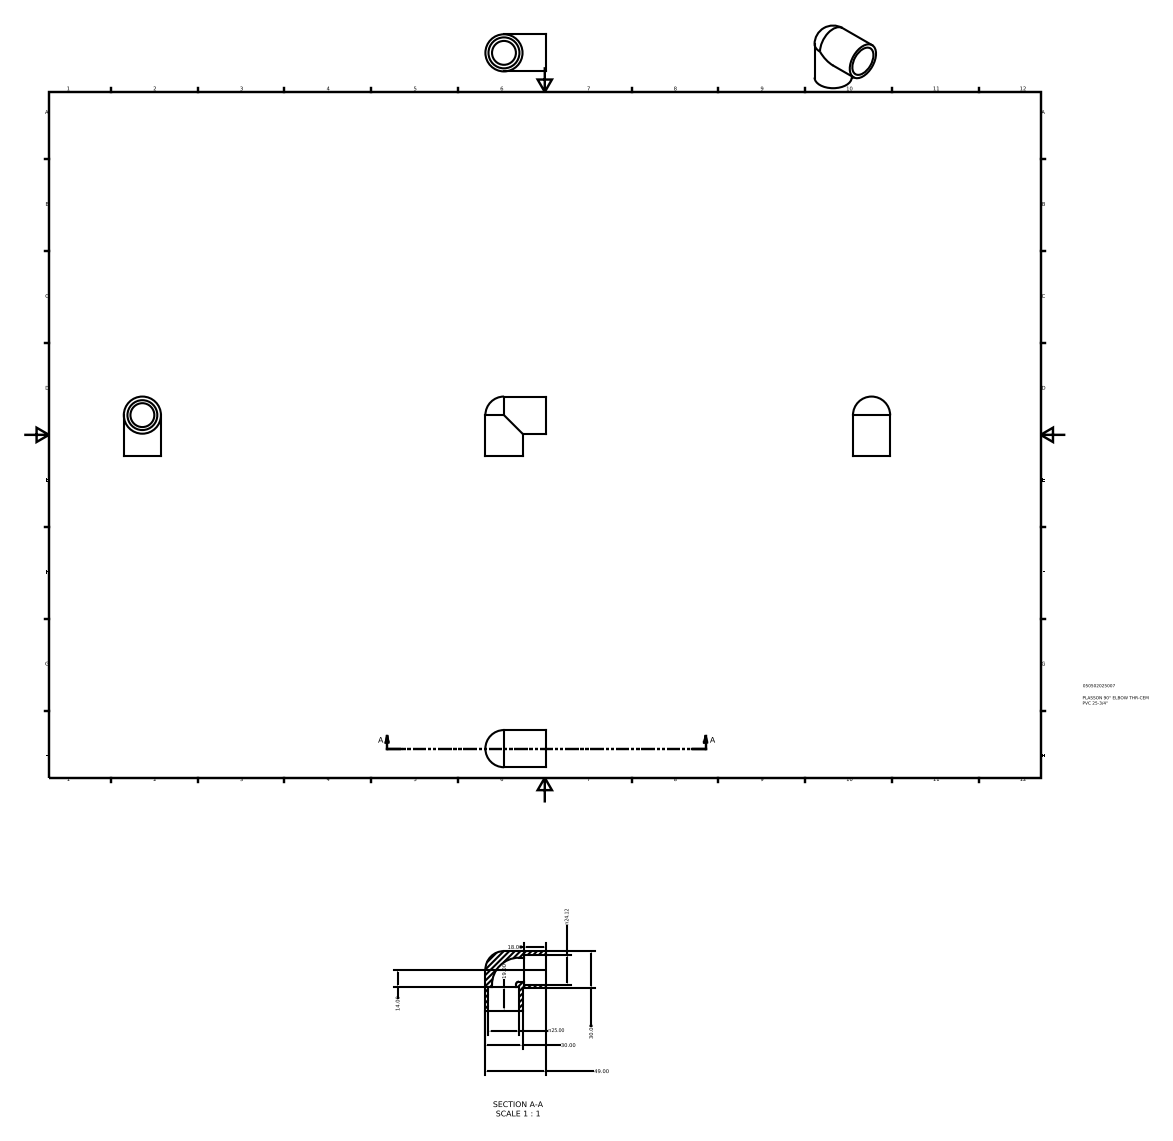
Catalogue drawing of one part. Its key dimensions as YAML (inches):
part_name: "050502025007"
step_written_by: "Autodesk Inventor 2015 (AUTOMOTIVE_DESIGN)"
units: inches
bodies: {solids: 1, faces: 12, planar: 4, cylindrical: 6, other: 2}
overall_size: [1.929, 1.89, 1.181]
volume: 1.317
surface_area: 17.53
round_holes:
  - {diameter: 0.759, count: 2}
  - {diameter: 0.95, count: 1}
  - {diameter: 0.984, count: 1}
round_bosses_or_shafts:
  - {diameter: 1.181, count: 2}
face_to_face_distances: [0.748, 0.709]
